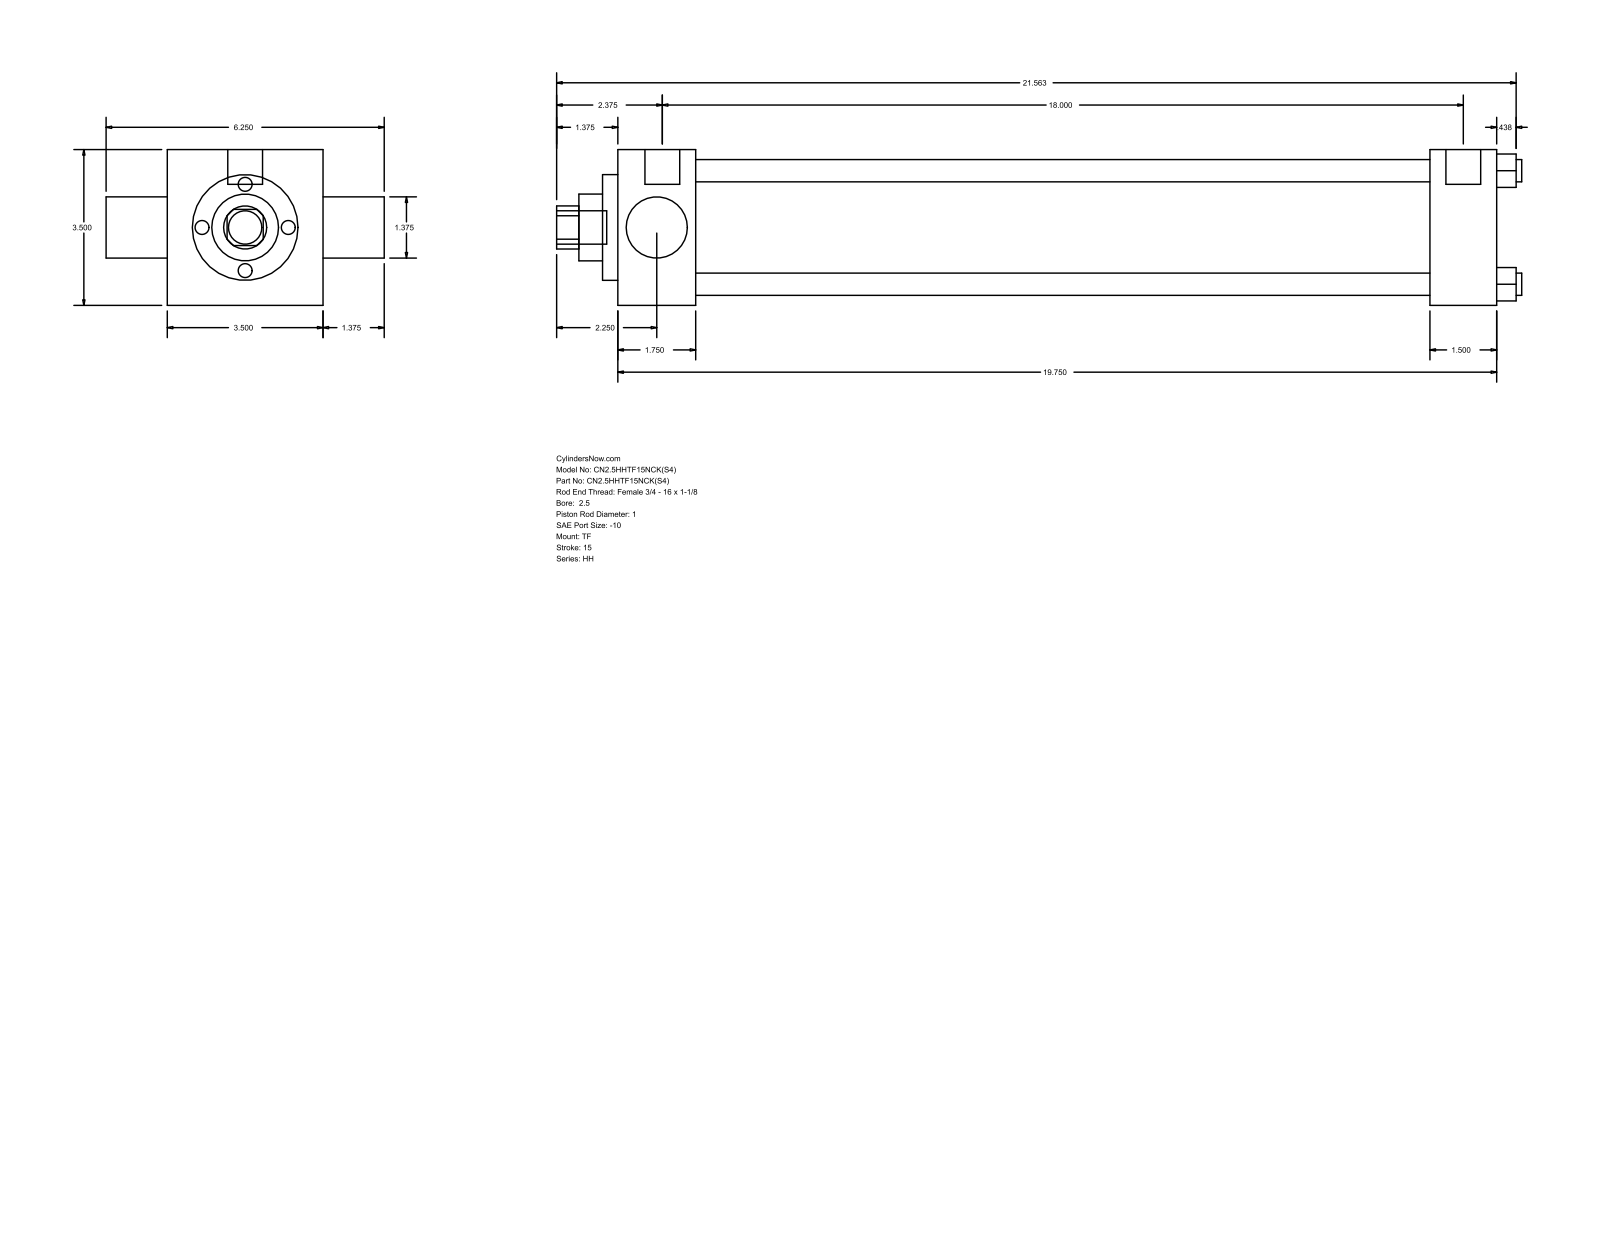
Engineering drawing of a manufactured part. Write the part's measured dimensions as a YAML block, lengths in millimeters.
part_name: "HH_TF__0250_1"
step_written_by: "GSSL Pune (CONFIG_CONTROL_DESIGN)"
units: millimeters
bodies: {solids: 0, faces: 86, planar: 61, cylindrical: 25, other: 0}
overall_size: [550.86, 158.75, 88.9]
round_holes:
  - {diameter: 12.7, count: 4}
  - {diameter: 25.4, count: 1}
  - {diameter: 34.92, count: 1}
  - {diameter: 38.1, count: 1}
  - {diameter: 60.33, count: 1}
  - {diameter: 73.03, count: 1}
round_bosses_or_shafts:
  - {diameter: 5.56, count: 3}
  - {diameter: 19.84, count: 2}
  - {diameter: 19.05, count: 1}
partial_cylinders:
  - {radius: 12.29, count: 1}
face_to_face_distances: [88.9, 501.66, 44.46, 457.2, 463.56, 419.1, 38.1, 34.93, 123.83, 8.73]
hole_center_spacings: [45.79, 64.76, 91.58]
